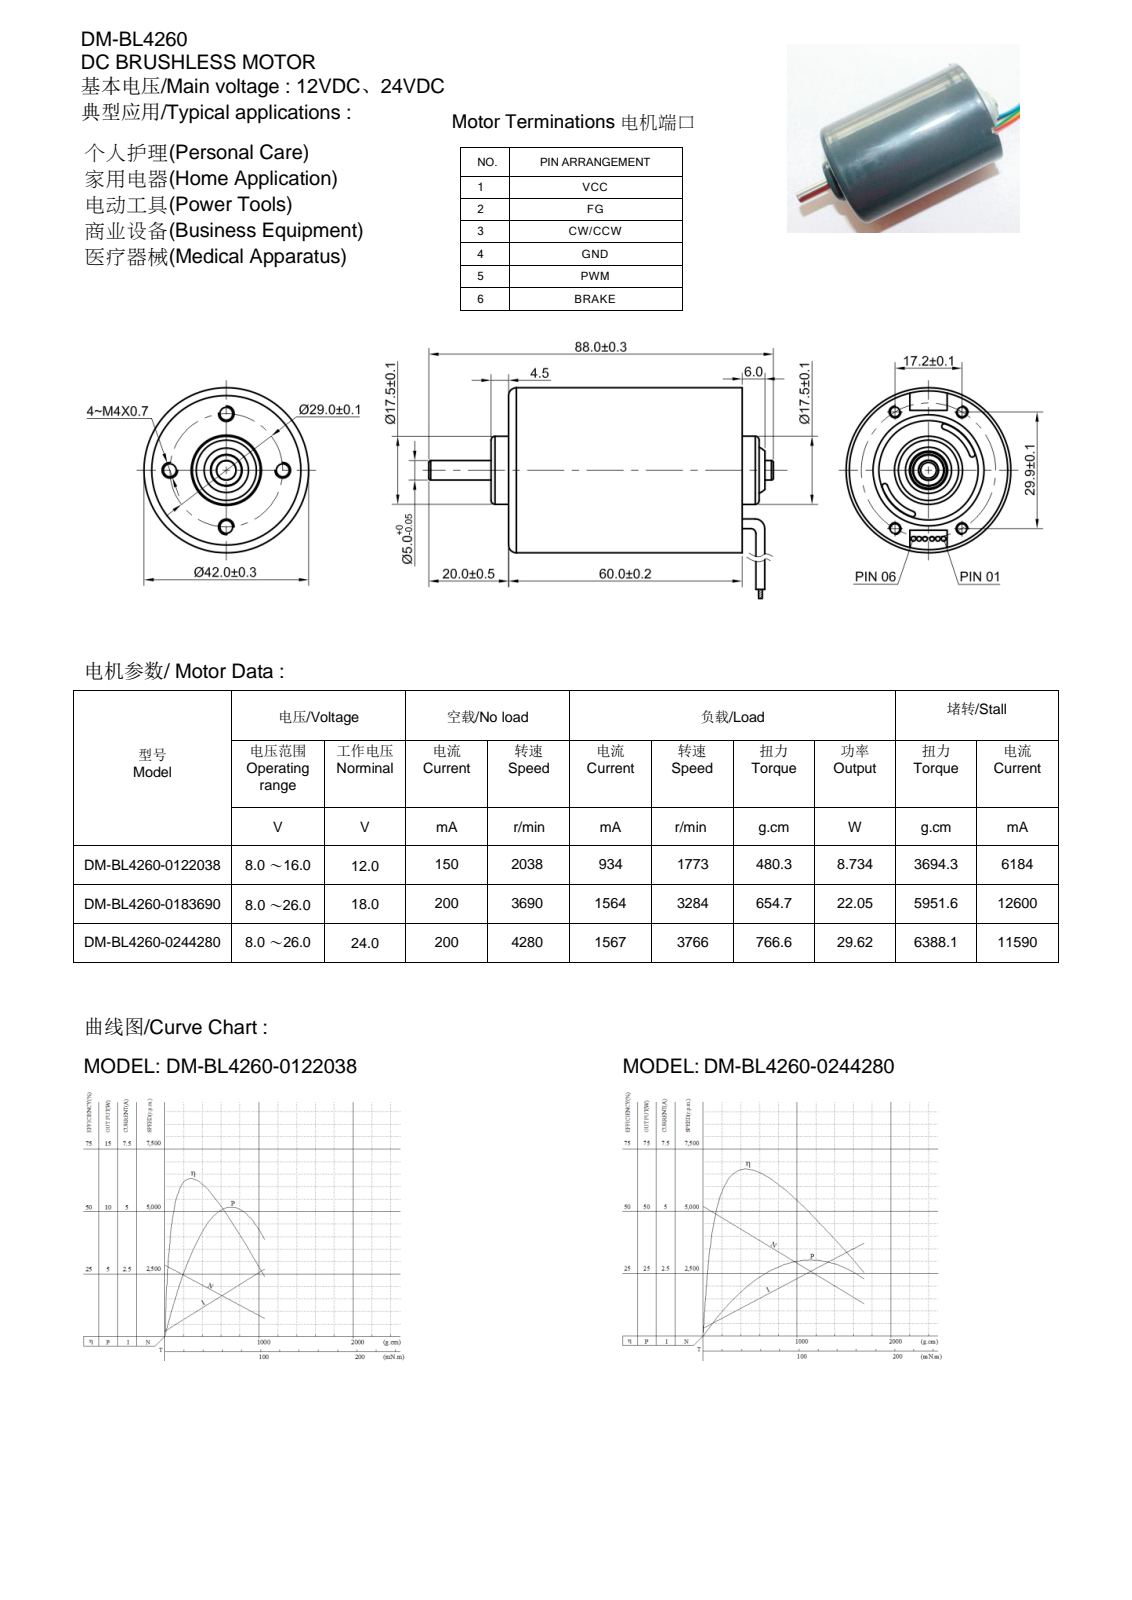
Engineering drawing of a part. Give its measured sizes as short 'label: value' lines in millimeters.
name: 5-83Цб; BL4260-3D
written by: SolidWorks 2020 (AUTOMOTIVE_DESIGN)
unit: mm
bodies: 6 solids, 197 faces (55 planar, 92 cylindrical, 50 other)
size: 83 × 42.1 × 42.1
volume: 15 507 mm³; area: 24 460 mm²
holes: 8× ⌀3.1, 2× ⌀3.3, 1× ⌀5, 1× ⌀11, 1× ⌀13.6, 1× ⌀16, 1× ⌀27, 1× ⌀39.7
bosses: 2× ⌀4.5, 1× ⌀42.1, 1× ⌀40.7, 1× ⌀28.5, 1× ⌀17.5, 1× ⌀7.4
rounds: 4× R0.7, 1× R11.25, 1× R12.65, 1× R19.35
face distances: 1.2, 57.1, 55.9, 1.5, 58.6, 58.3, 4.8, 3.6, 62.1, 62
hole spacings: 17, 8.94, 14.82, 23.44, 27.91, 6.99, 7, 14.5
